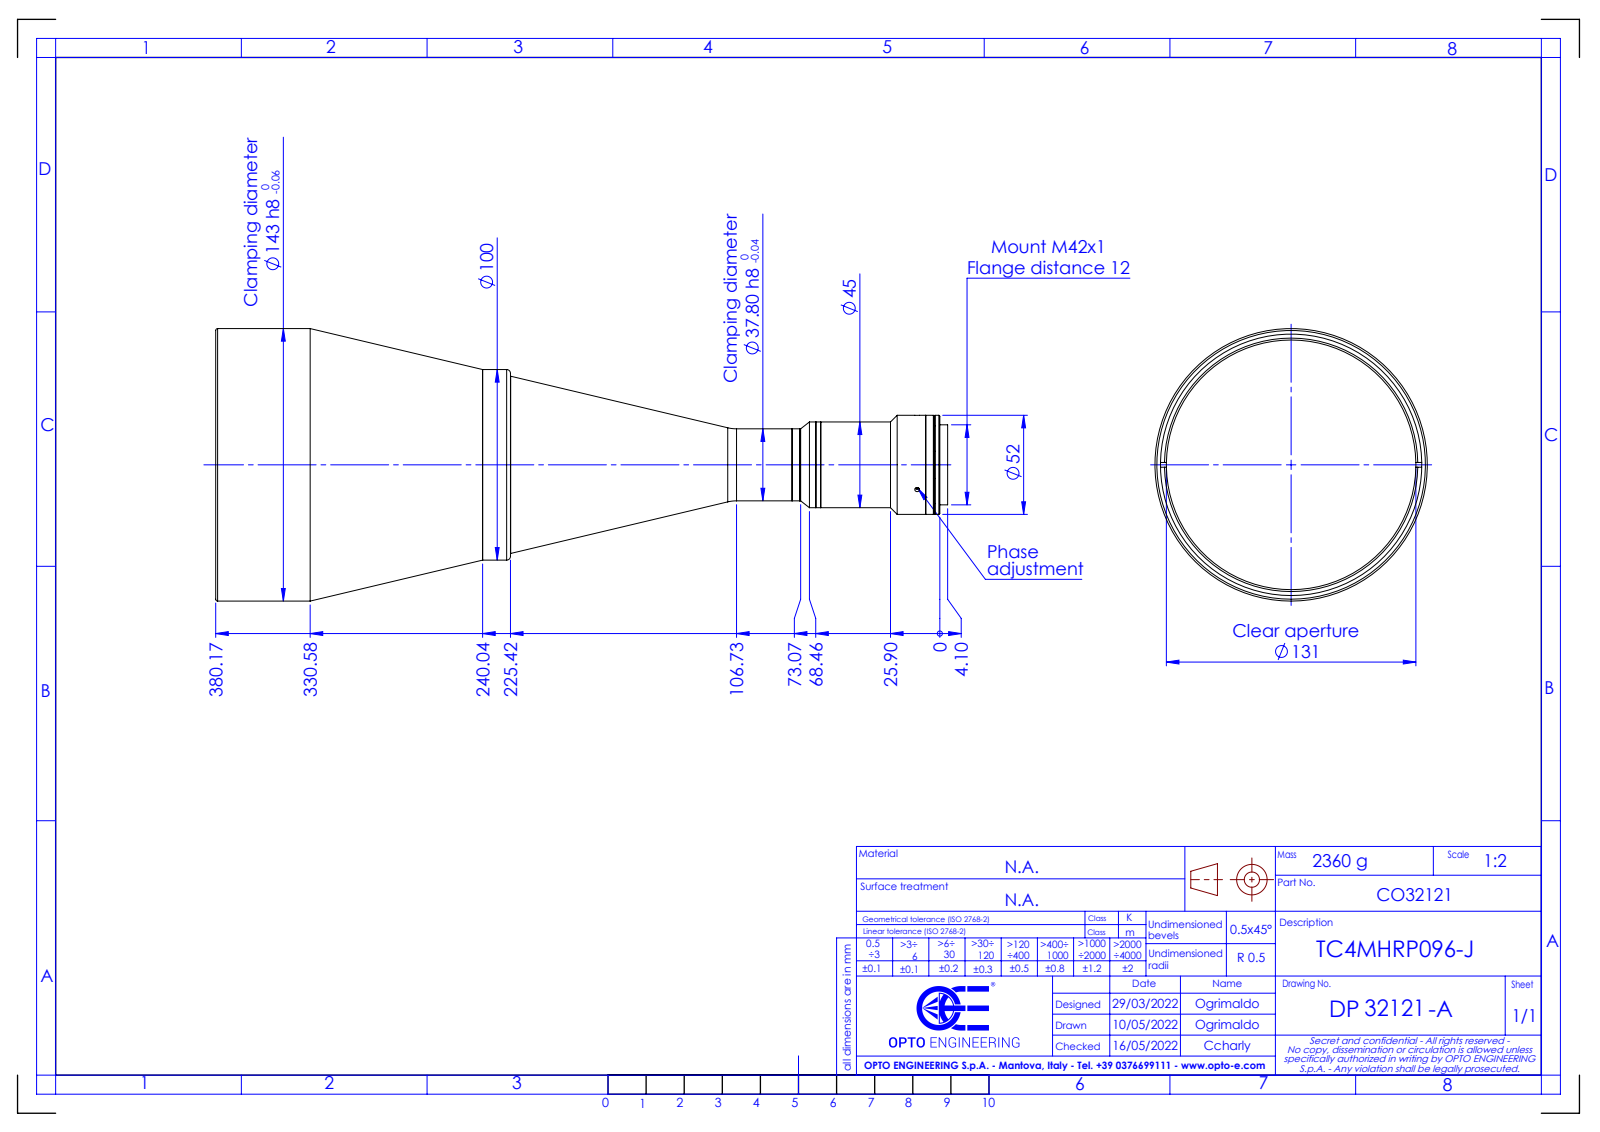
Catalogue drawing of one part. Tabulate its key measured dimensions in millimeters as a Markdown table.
| quantity | value |
| --- | --- |
| part name | DP32121-A_TC4MHRP096-J |
| STEP written by | SolidWorks 2021 (CONFIG_CONTROL_DESIGN) |
| units | millimeters |
| bodies | 0 solids, 93 faces (21 planar, 48 cylindrical, 24 other) |
| overall size | 384.27 × 143 × 143 |
| round holes (diameter × count) | 2.5 × 3, 38 × 1, 41 × 1, 131 × 1, 137.2 × 1 |
| round bosses / shafts (diameter × count) | 143 × 1, 100 × 1, 93 × 1, 52 × 1, 51.8 × 1, 45 × 1, 42 × 1, 37.8 × 1 |
| main face-to-face distances | 139.41, 376.89, 237.48, 0.72, 140.13, 377.61, 376.77, 376.05, 236.64, 0.84 |
